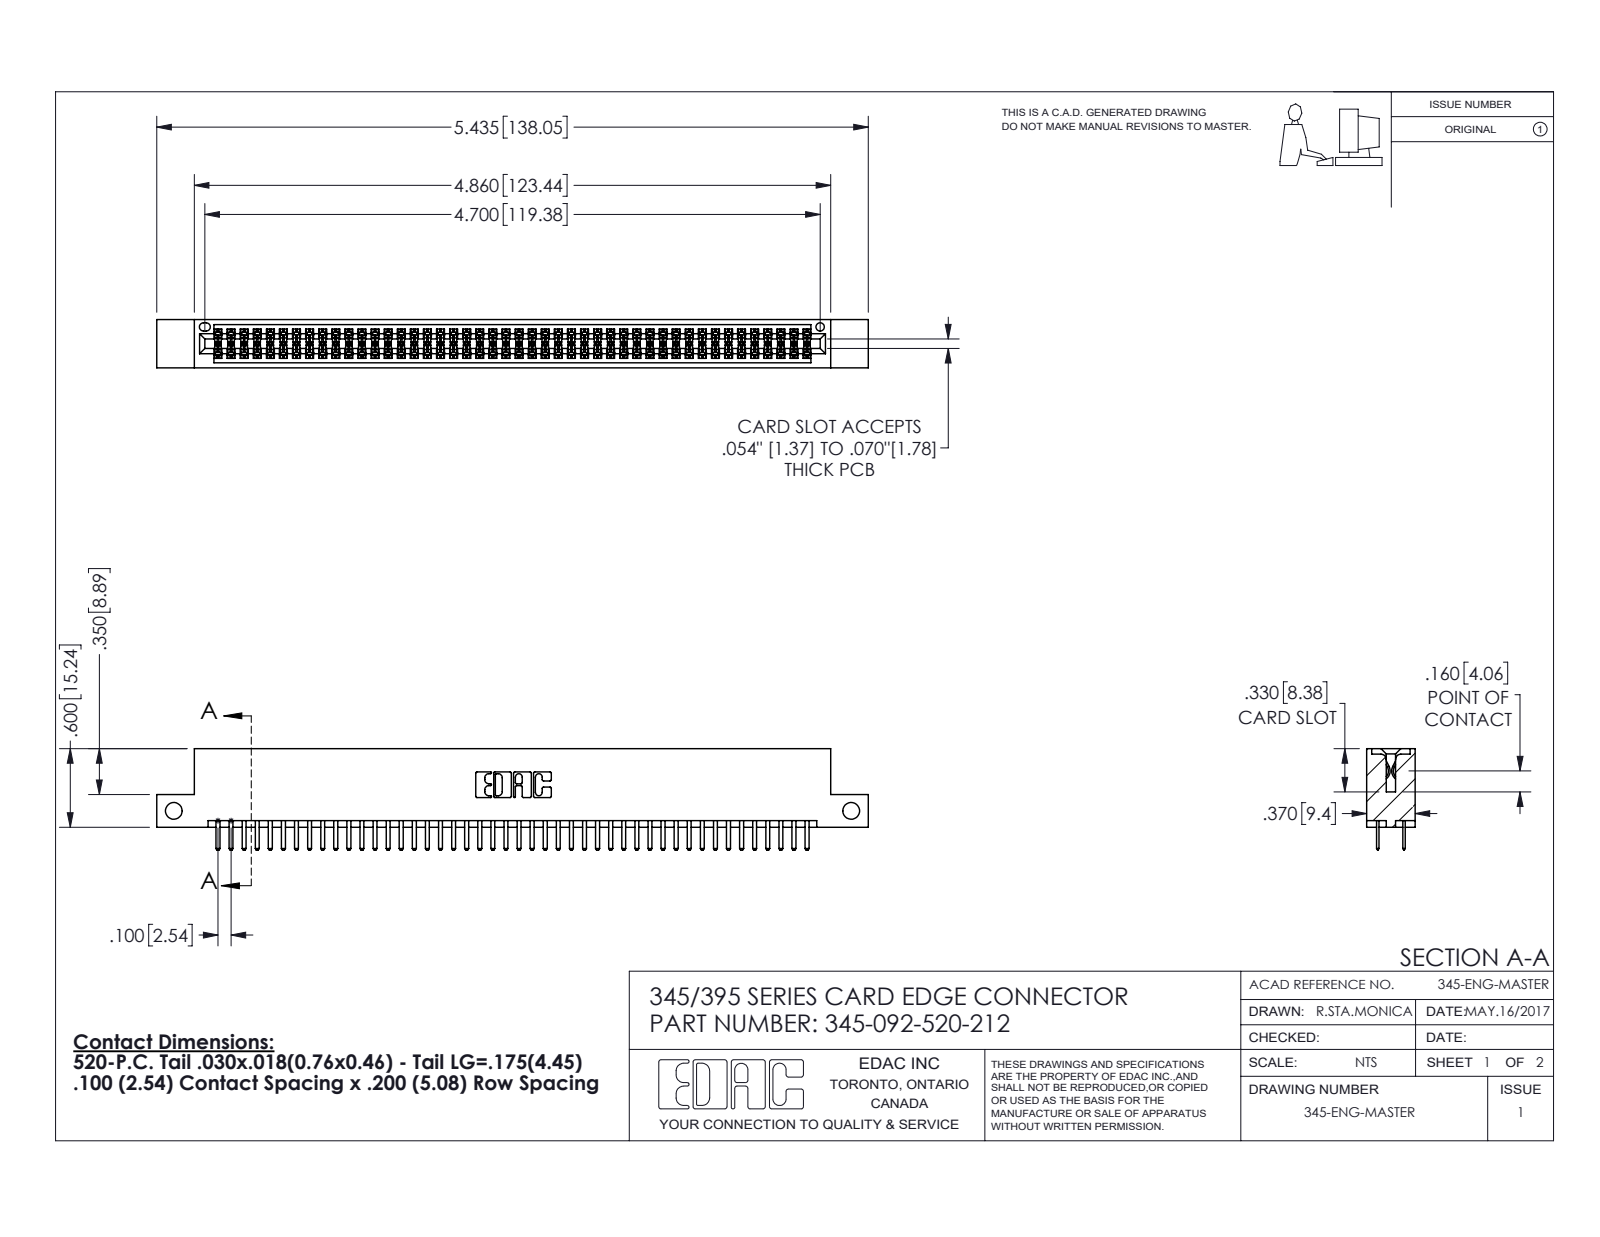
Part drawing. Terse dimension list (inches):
name: 345-292-001_345-293-120; 345 Part_Flush Mounting Lugs - Side Mount; 345-092-520-212
written by: SolidWorks 2016 (CONFIG_CONTROL_DESIGN)
unit: in
bodies: 93 solids, 5094 faces (3300 planar, 1794 cylindrical, 0 other)
size: 5.435 × 0.775 × 0.37
volume: 0.813 in³; area: 30.29 in²
holes: 2× ⌀0.128, 1× ⌀0.064
rounds: 138× R0.006, 96× R0.01, 22× R0.01, 6× R0.007, 6× R0.031, 3× R0.026, 2× R0.014, 2× R0.019
face distances: 0.298, 0.072, 0.2, 0.37, 0.098, 0.272, 0.025, 0.225, 0.022, 0.072
hole spacings: 5.175
